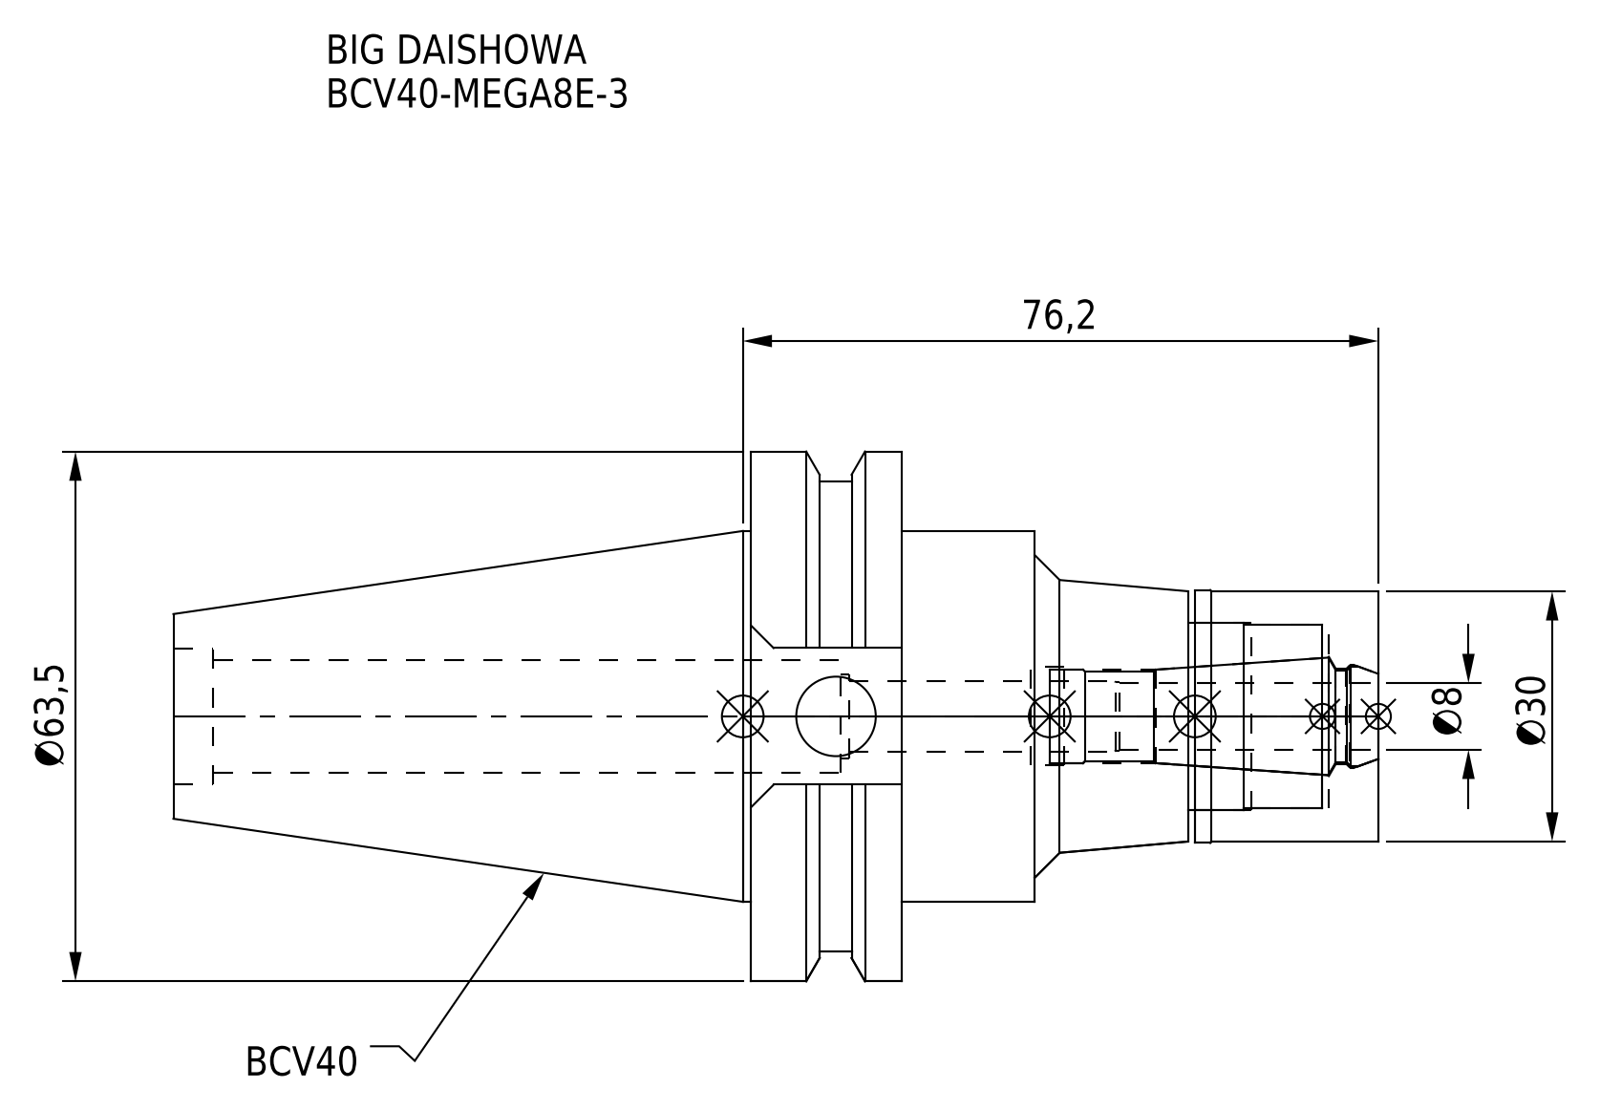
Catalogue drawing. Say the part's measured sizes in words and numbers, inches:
The part is named "BCV40ME08030-008_ASM.stp; BCV40-MEGA8E-3-080.stp; DXF_TEMP_ASSY_ASM_4_ASM.stp; BCV40-MEGA8E-3-080-FreeParts (+3 more)". Its 3-D file was written by "SolidWorks 2019 (CONFIG_CONTROL_DESIGN)". It is 2 solids with 93 faces: 31 planar, 42 cylindrical and 20 other. Overall it measures 5.687 by 2.5 by 2.415 inches. Its volume is 9.409 cubic inches and its surface area 49.22 square inches. Round holes: 1 of diameter 0.331, 1 of diameter 0.375, 1 of diameter 0.394, 1 of diameter 0.441, 1 of diameter 0.449, 1 of diameter 0.465, 1 of diameter 0.484, 1 of diameter 0.535, 1 of diameter 0.643, 1 of diameter 0.866, 1 of diameter 0.886. Round bosses or shafts: 1 of diameter 2.5, 1 of diameter 2.219, 1 of diameter 1.75, 1 of diameter 1.193, 1 of diameter 1.181. The main face-to-face distances are 0.711, 2.25, 2.961, 1.622, 0.628, 1.339, 0.236, 0.866, 0.756, 1.384.
